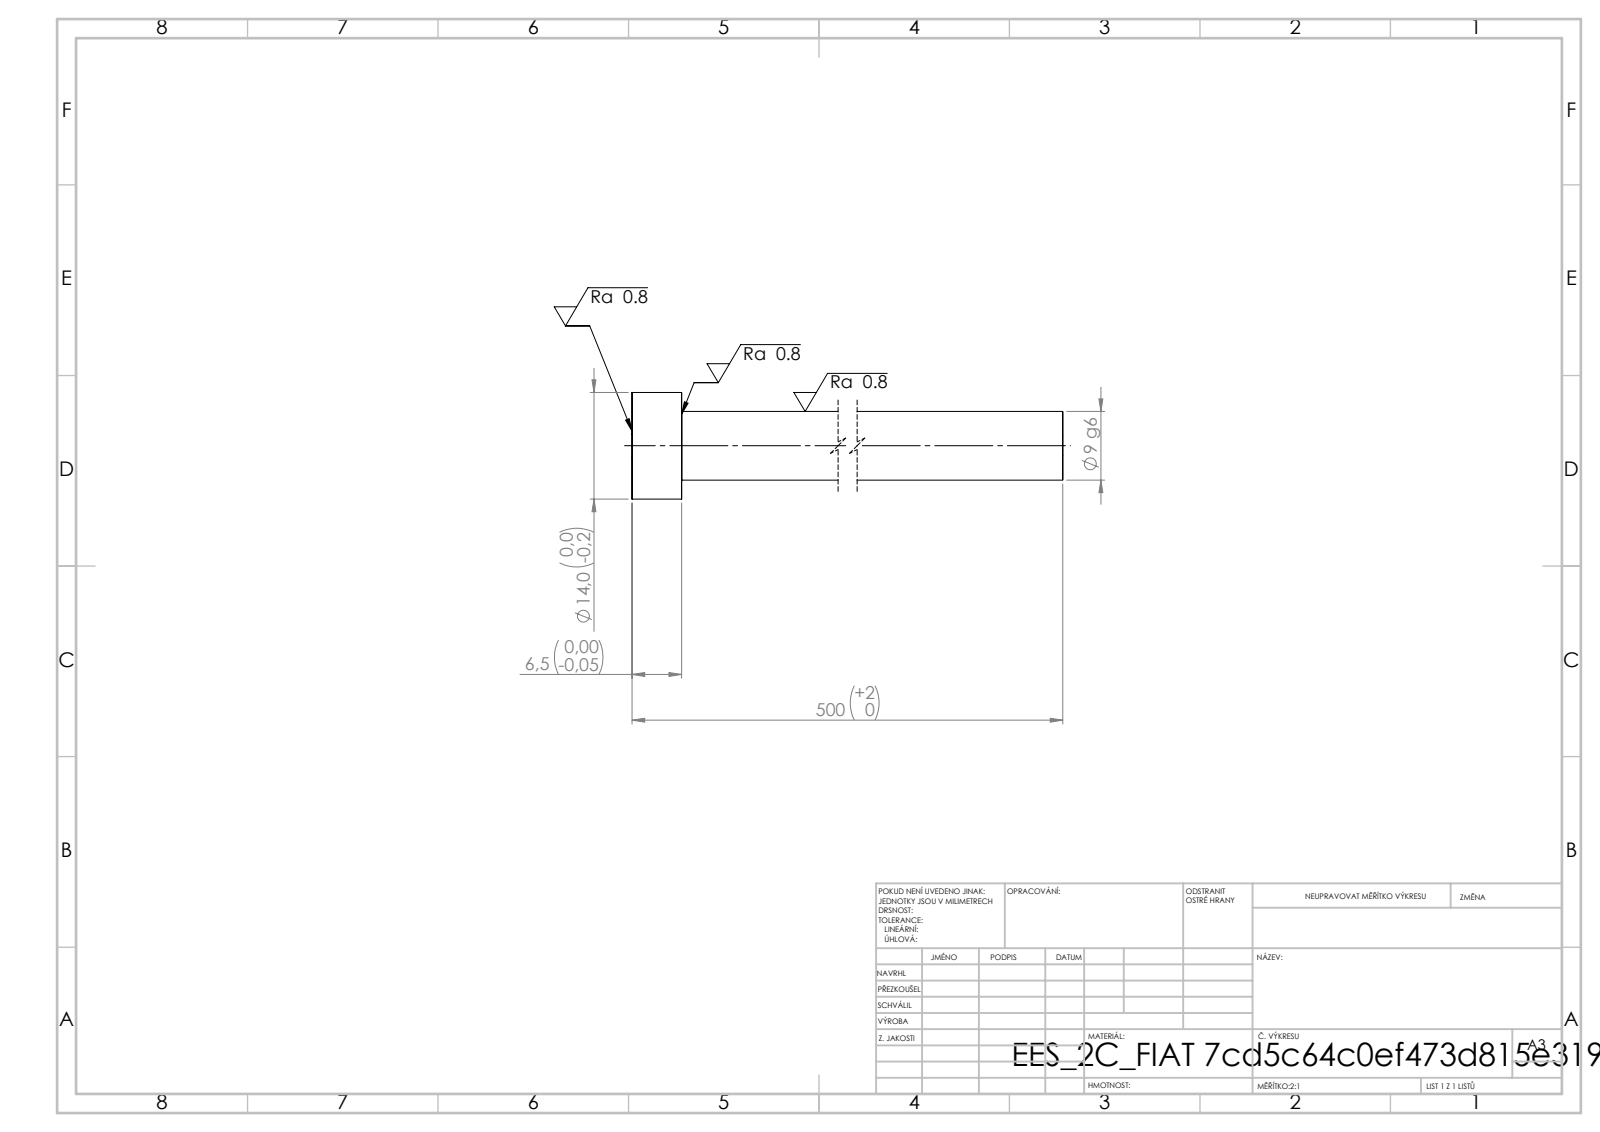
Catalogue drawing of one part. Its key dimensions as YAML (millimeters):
step_written_by: "SolidWorks 2019 (CONFIG_CONTROL_DESIGN)"
units: millimeters
bodies: {solids: 1, faces: 7, planar: 3, cylindrical: 4, other: 0}
overall_size: [500, 14, 14]
volume: 32396
surface_area: 14547
round_bosses_or_shafts:
  - {diameter: 14, count: 1}
  - {diameter: 9, count: 1}
face_to_face_distances: [6.5, 500, 493.5]
